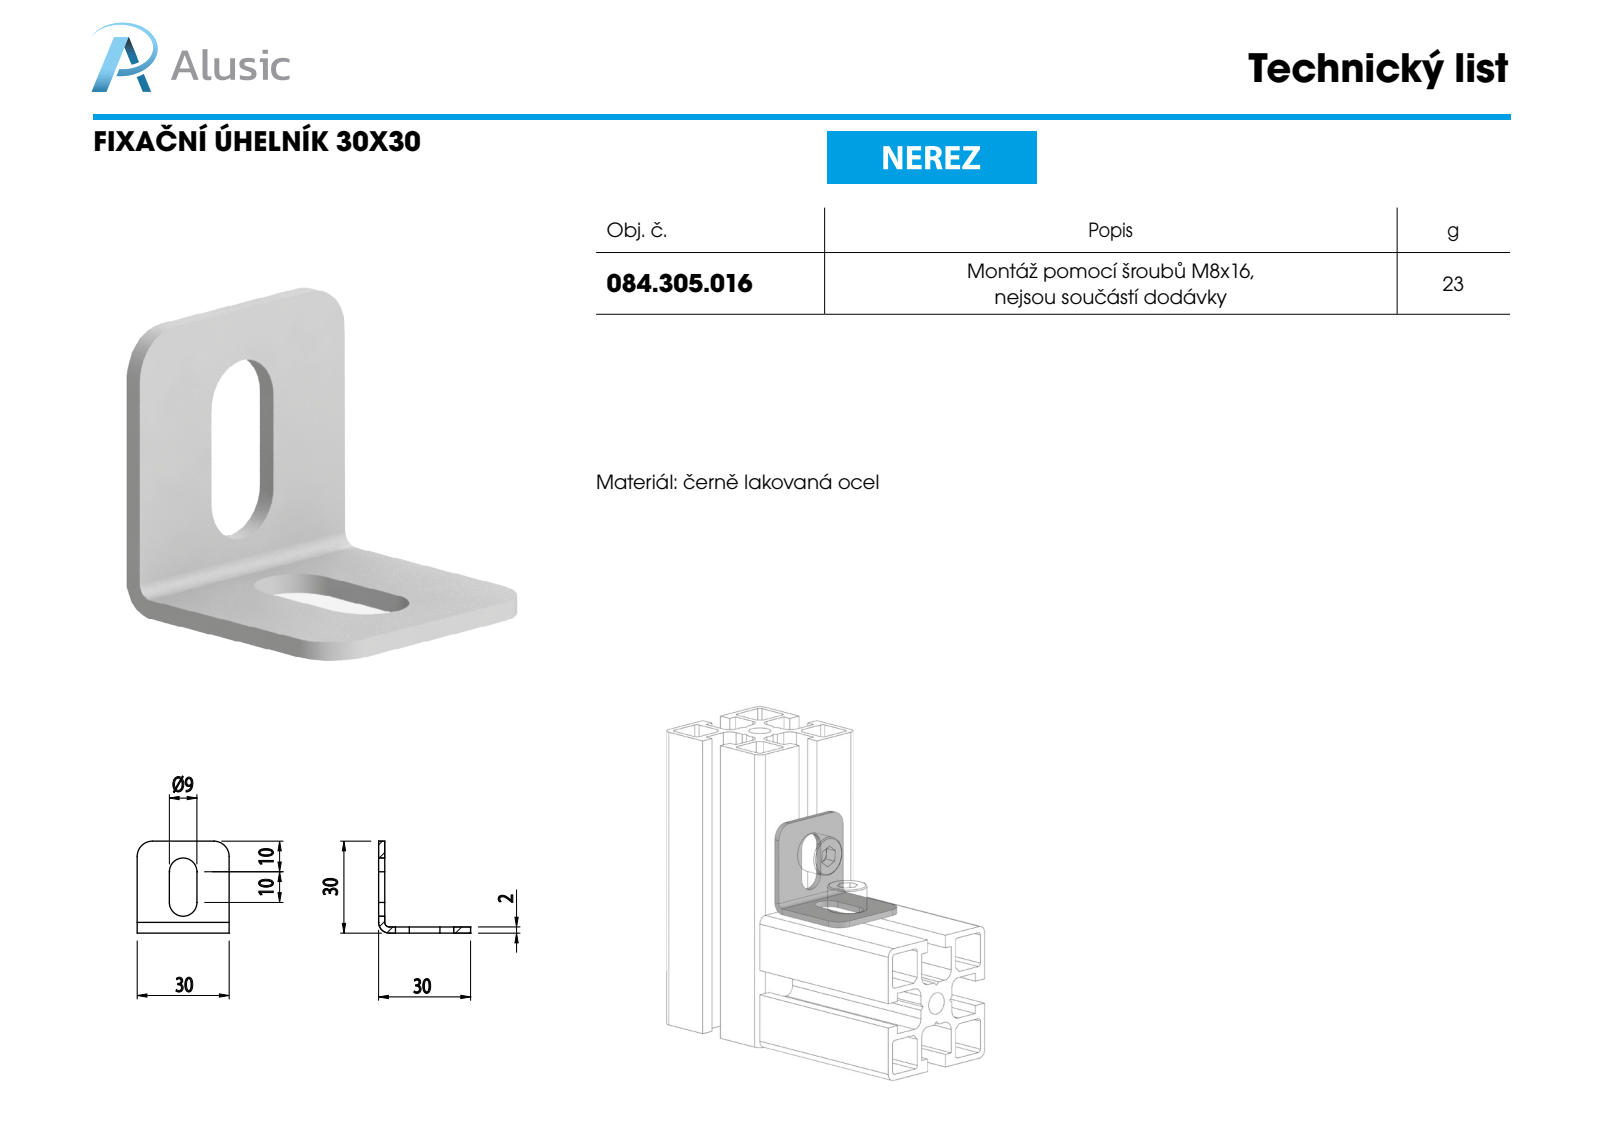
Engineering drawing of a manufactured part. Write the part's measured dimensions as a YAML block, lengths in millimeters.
part_name: "084.305.016"
step_written_by: "SolidWorks 2011 (CONFIG_CONTROL_DESIGN)"
units: millimeters
bodies: {solids: 1, faces: 26, planar: 16, cylindrical: 10, other: 0}
overall_size: [30, 30, 30]
volume: 2758
surface_area: 3282
partial_cylinders:
  - {radius: 4.5, count: 4}
  - {radius: 5, count: 4}
  - {radius: 1.5, count: 1}
  - {radius: 3.5, count: 1}
face_to_face_distances: [2, 30, 10.5, 19.5, 28, 9]
